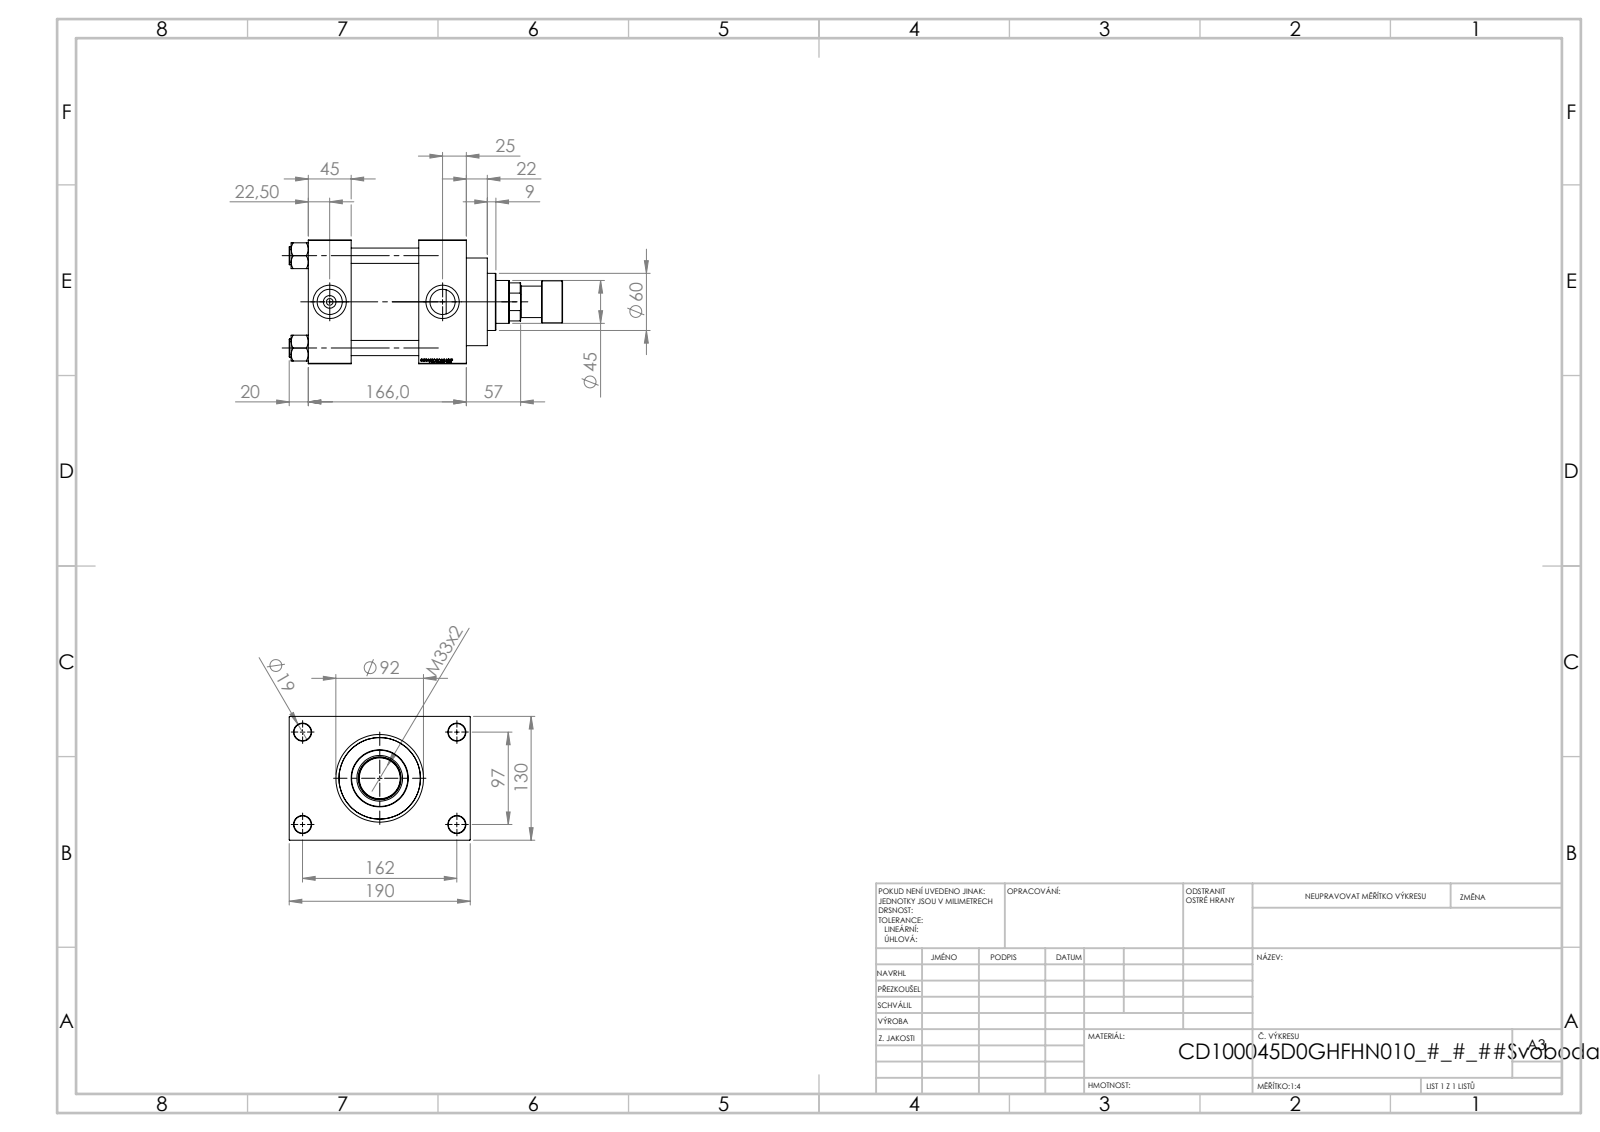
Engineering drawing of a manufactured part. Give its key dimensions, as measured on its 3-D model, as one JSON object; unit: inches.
{"part_name": "V215CD_NUT_M5_D; V215CR_ROD_END_F; V215CD_VCP_D; V215CD_D_TYCINKA (+2 more)", "step_written_by": "SolidWorks 2019 (CONFIG_CONTROL_DESIGN)", "units": "inches", "bodies": {"solids": 12, "faces": 1164, "planar": 548, "cylindrical": 92, "other": 524}, "overall_size": [11.299, 7.48, 5.118], "volume_in3": 161.3, "surface_area_in2": 563, "round_holes": [[0.63, 4], [0.709, 4], [0.276, 2], [1.041, 2], [1.378, 2], [1.24, 1], [1.772, 1], [1.89, 1], [2.992, 1], [3.366, 1], [3.937, 1]], "round_bosses_or_shafts": [[0.748, 4], [4.173, 1], [3.622, 1], [2.362, 1], [1.732, 1], [1.299, 1]], "face_to_face_distances": [5.118, 4.567, 1.772, 2.795, 6.535, 4.764, 1.969, 1.181, 6.299, 2.756], "hole_center_spacings": [1.281, 2.698, 3.717, 3.815, 4.026, 5.096, 6.367, 3.819]}
